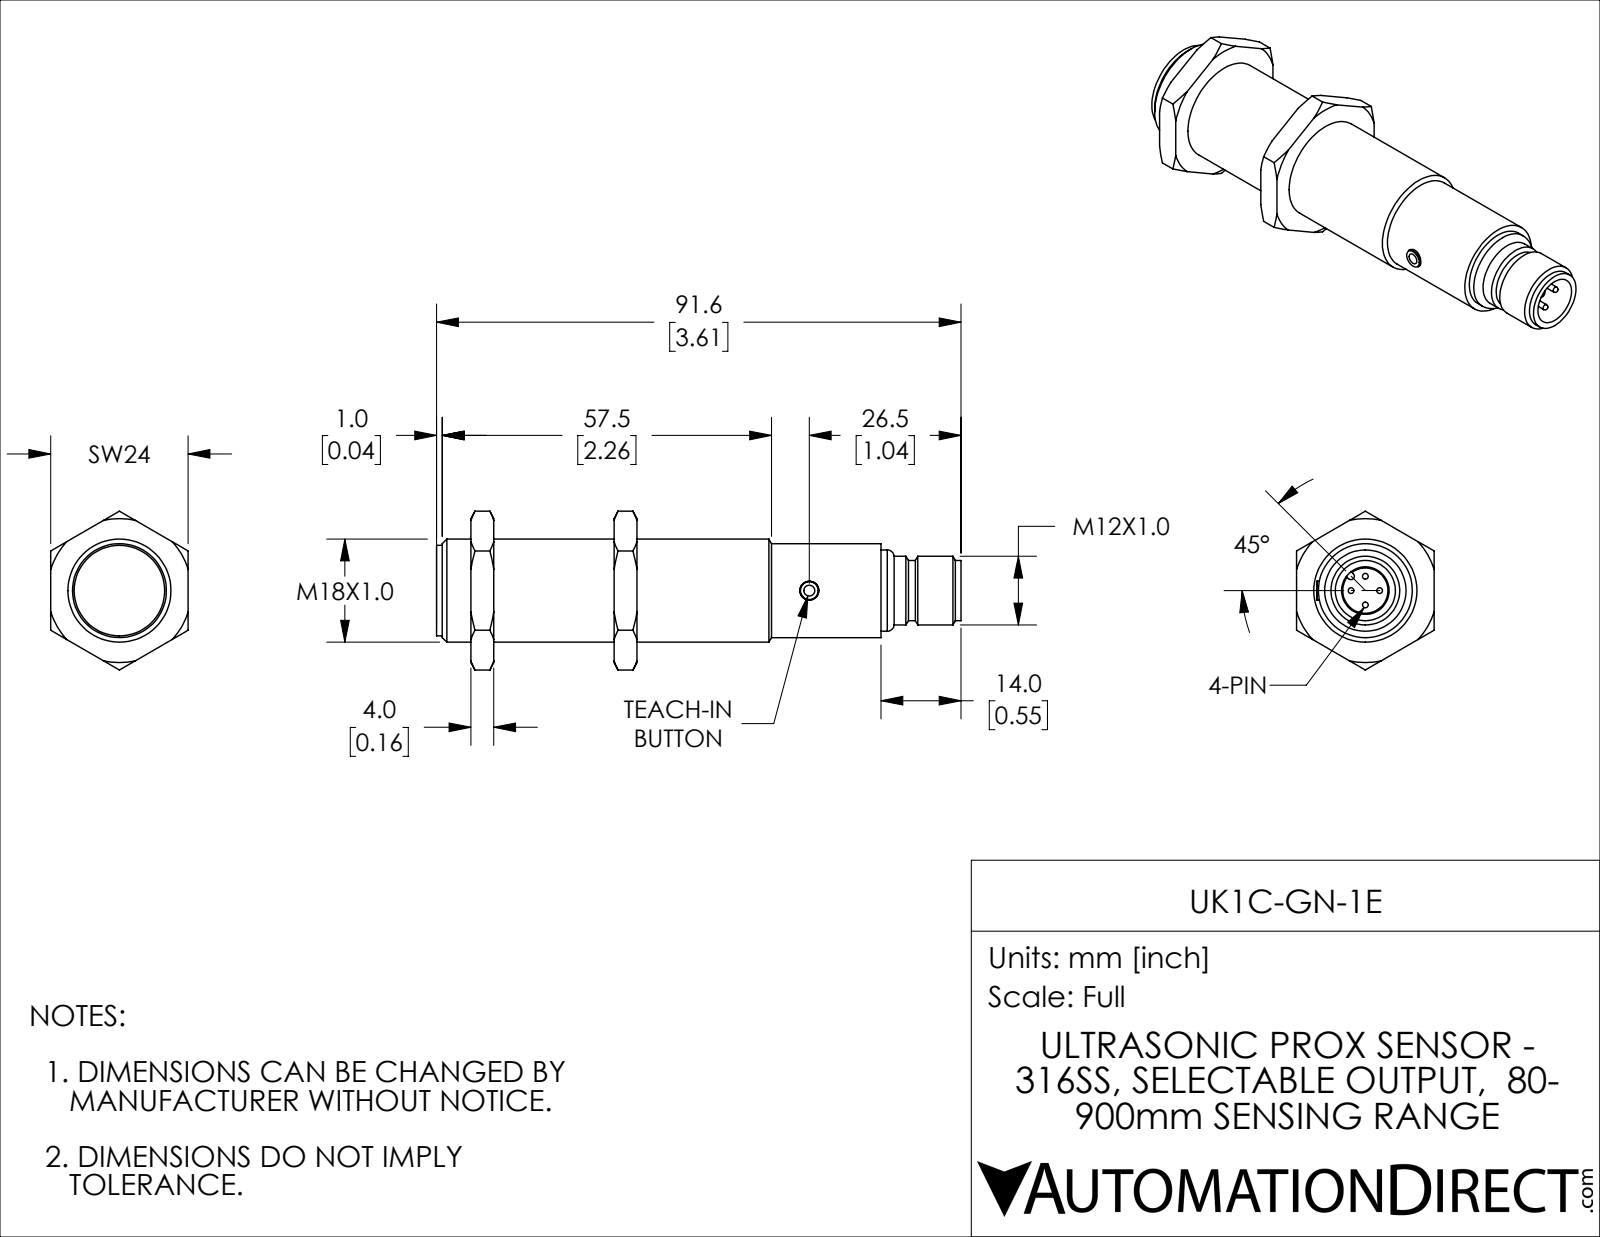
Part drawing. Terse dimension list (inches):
name: UK1C-GN-1E
written by: SolidWorks 2018 (AUTOMOTIVE_DESIGN)
unit: in
bodies: 4 solids, 113 faces (27 planar, 35 cylindrical, 51 other)
size: 3.606 × 1.091 × 0.945
volume: 1.338 in³; area: 11.97 in²
holes: 1× ⌀0.13, 1× ⌀0.327, 1× ⌀0.709
bosses: 4× ⌀0.039, 1× ⌀0.646, 1× ⌀0.622, 1× ⌀0.559, 1× ⌀0.472, 1× ⌀0.413
rounds: 1× R0.024
face distances: 0.984, 0.157, 0.945, 1.142, 0.827, 0.236, 0.394, 1.22, 1.378, 3.055
